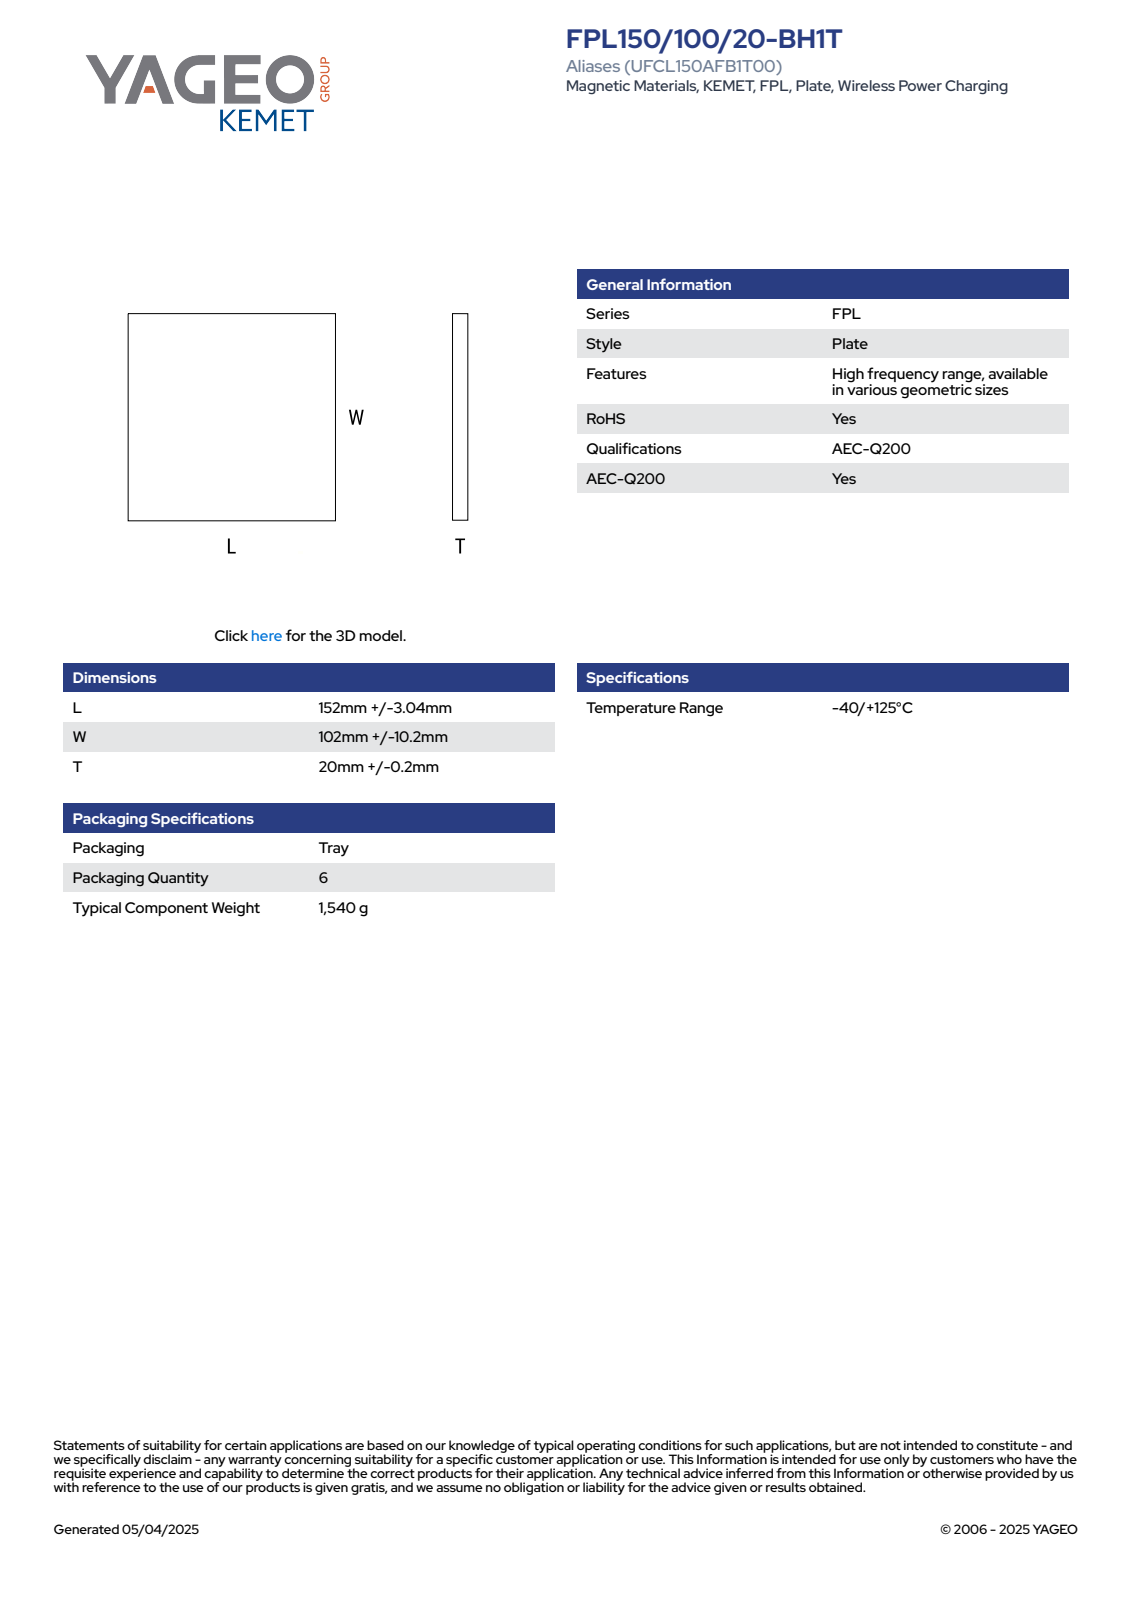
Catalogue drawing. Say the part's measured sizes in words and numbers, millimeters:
The part is named "FM_KP_L155.04W12.24T20.2". Its 3-D file was written by "SolidWorks 2020 (AUTOMOTIVE_DESIGN)". It is 4 solids with 63 faces: 63 planar, 0 cylindrical and 0 other. Overall it measures 155.04 by 23.77 by 20.2 millimeters. Its volume is 38 338 cubic millimeters and its surface area 12 562 square millimeters. The main face-to-face distances are 12.24, 20.2, 20.21, 155.04, 11.53, 23.77, 18.38, 6.85, 5.39, 75.28.
